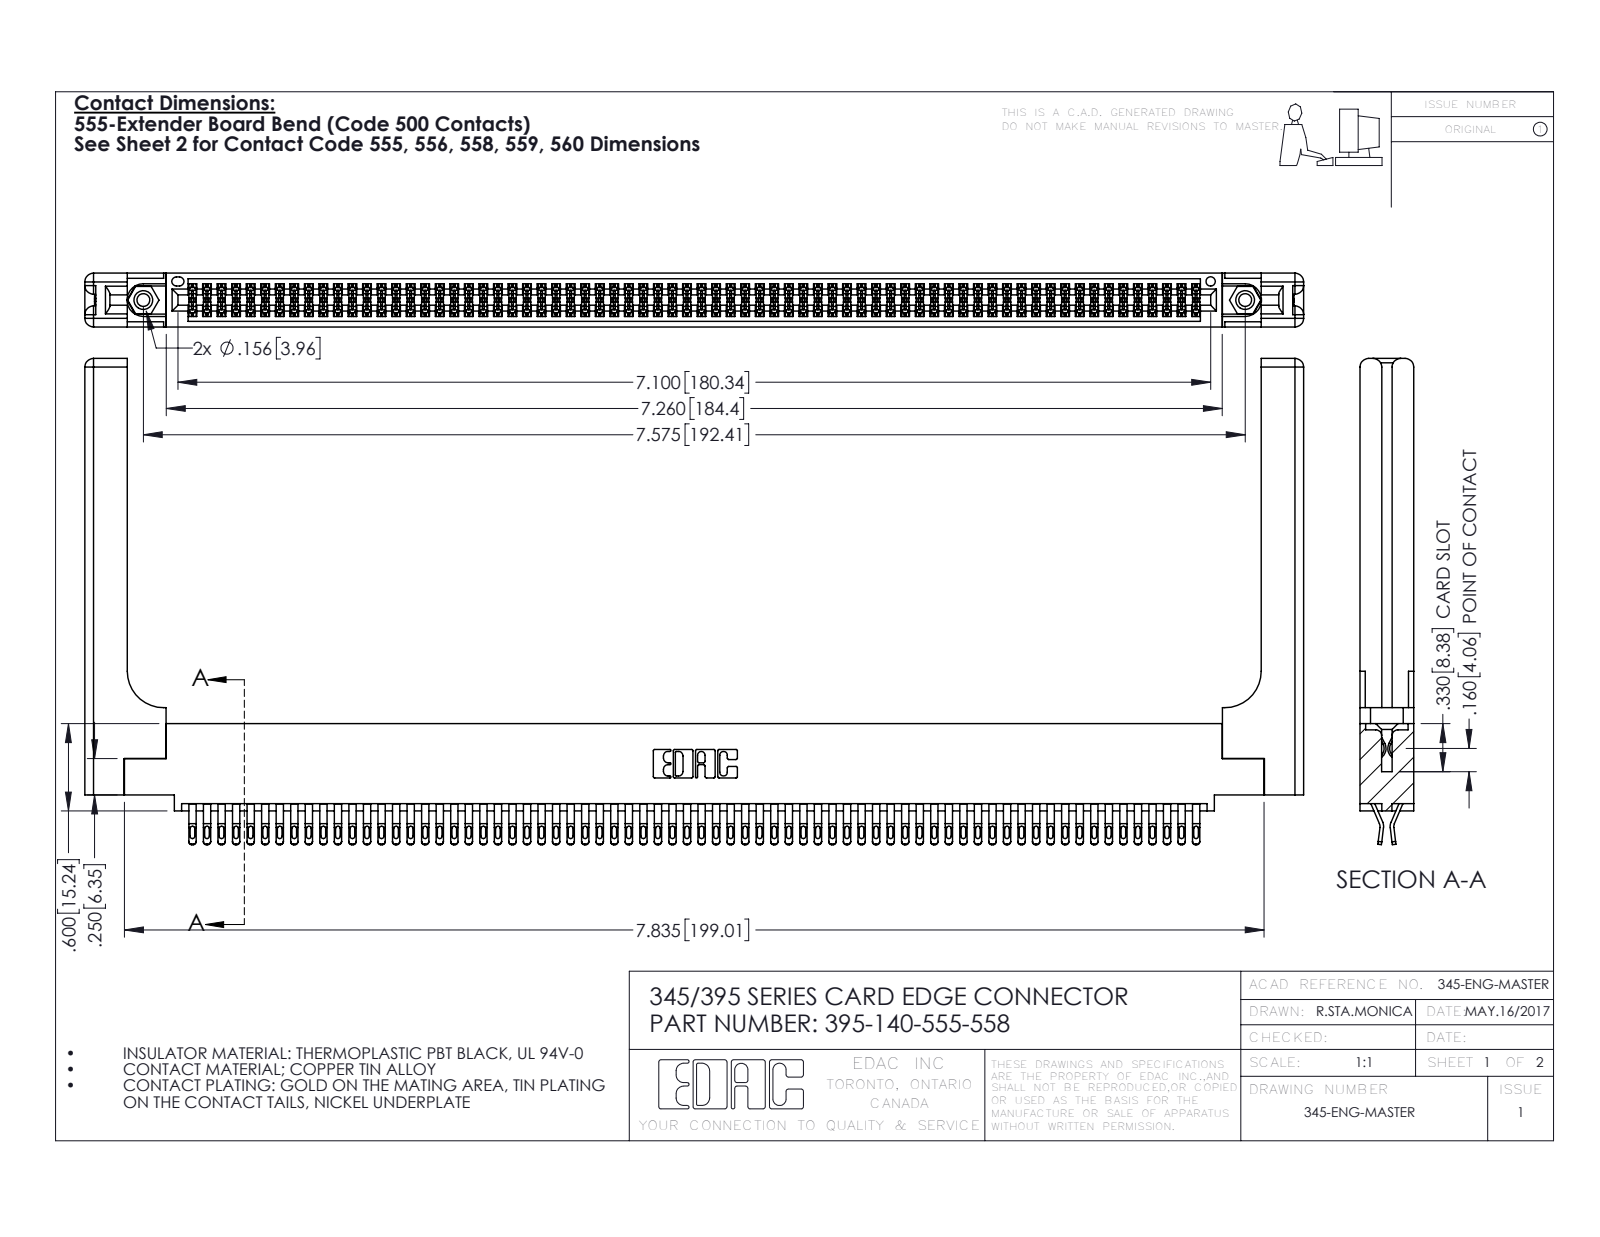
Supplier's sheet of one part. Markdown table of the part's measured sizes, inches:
| quantity | value |
| --- | --- |
| part name | 395-140-555-558; 345-250-001_345-250-001-102; 345-220-058_345-220-058; 345-292-001_555 Tail (+1 more) |
| STEP written by | SolidWorks 2016 (CONFIG_CONTROL_DESIGN) |
| units | inches |
| bodies | 145 solids, 8226 faces (4572 planar, 3594 cylindrical, 60 other) |
| overall size | 8.379 × 3.342 × 0.37 |
| volume | 1.815 in³ |
| surface area | 59.74 in² |
| round holes (diameter × count) | 0.089 × 2, 0.125 × 2, 0.156 × 2, 0.064 × 1 |
| round bosses / shafts (diameter × count) | 0.155 × 2 |
| partial cylindrical surfaces (radius × count) | 0.016 × 350, 0.02 × 280, 0.006 × 210, 0.01 × 22, 0.06 × 16, 0.007 × 6, 0.031 × 6, 0.026 × 3 |
| main face-to-face distances | 0.072, 0.298, 0.37, 0.025, 0.098, 0.272, 0.2, 0.225, 0.175, 0.148 |
| hole center spacings | 0.27, 7.339, 7.575 |
